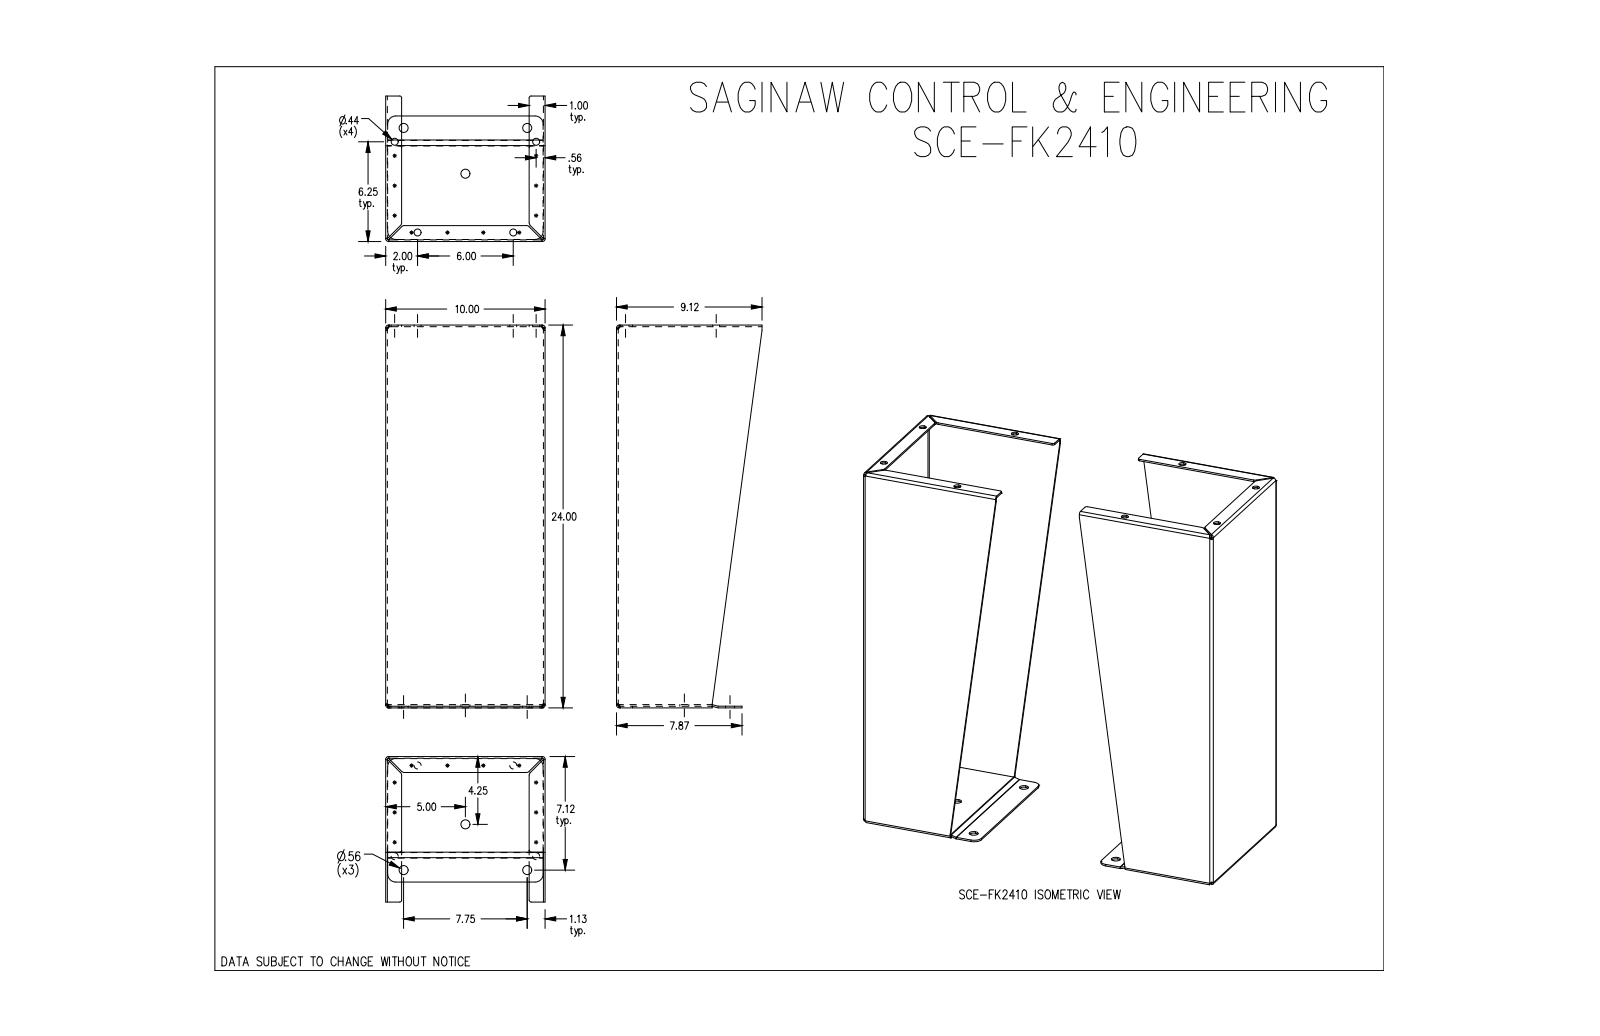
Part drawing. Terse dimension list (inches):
name: SCE-FK2410
written by: SolidWorks 2019 (CONFIG_CONTROL_DESIGN)
unit: in
bodies: 4 solids, 214 faces (96 planar, 86 cylindrical, 32 other)
size: 24 × 24 × 10
volume: 147.2 in³; area: 2 863 in²
holes: 8× ⌀0.437, 6× ⌀0.563
rounds: 16× R0.166, 10× R0.062, 10× R0.063, 8× R0.125, 8× R0.22, 8× R0.5
face distances: 0.104, 9.896, 23.896, 9.792, 10, 23.792, 24, 0.101, 23.893, 23.688
hole spacings: 1.035, 4.755, 4.867, 5.866, 6.614, 9.363, 10.646, 13.211
